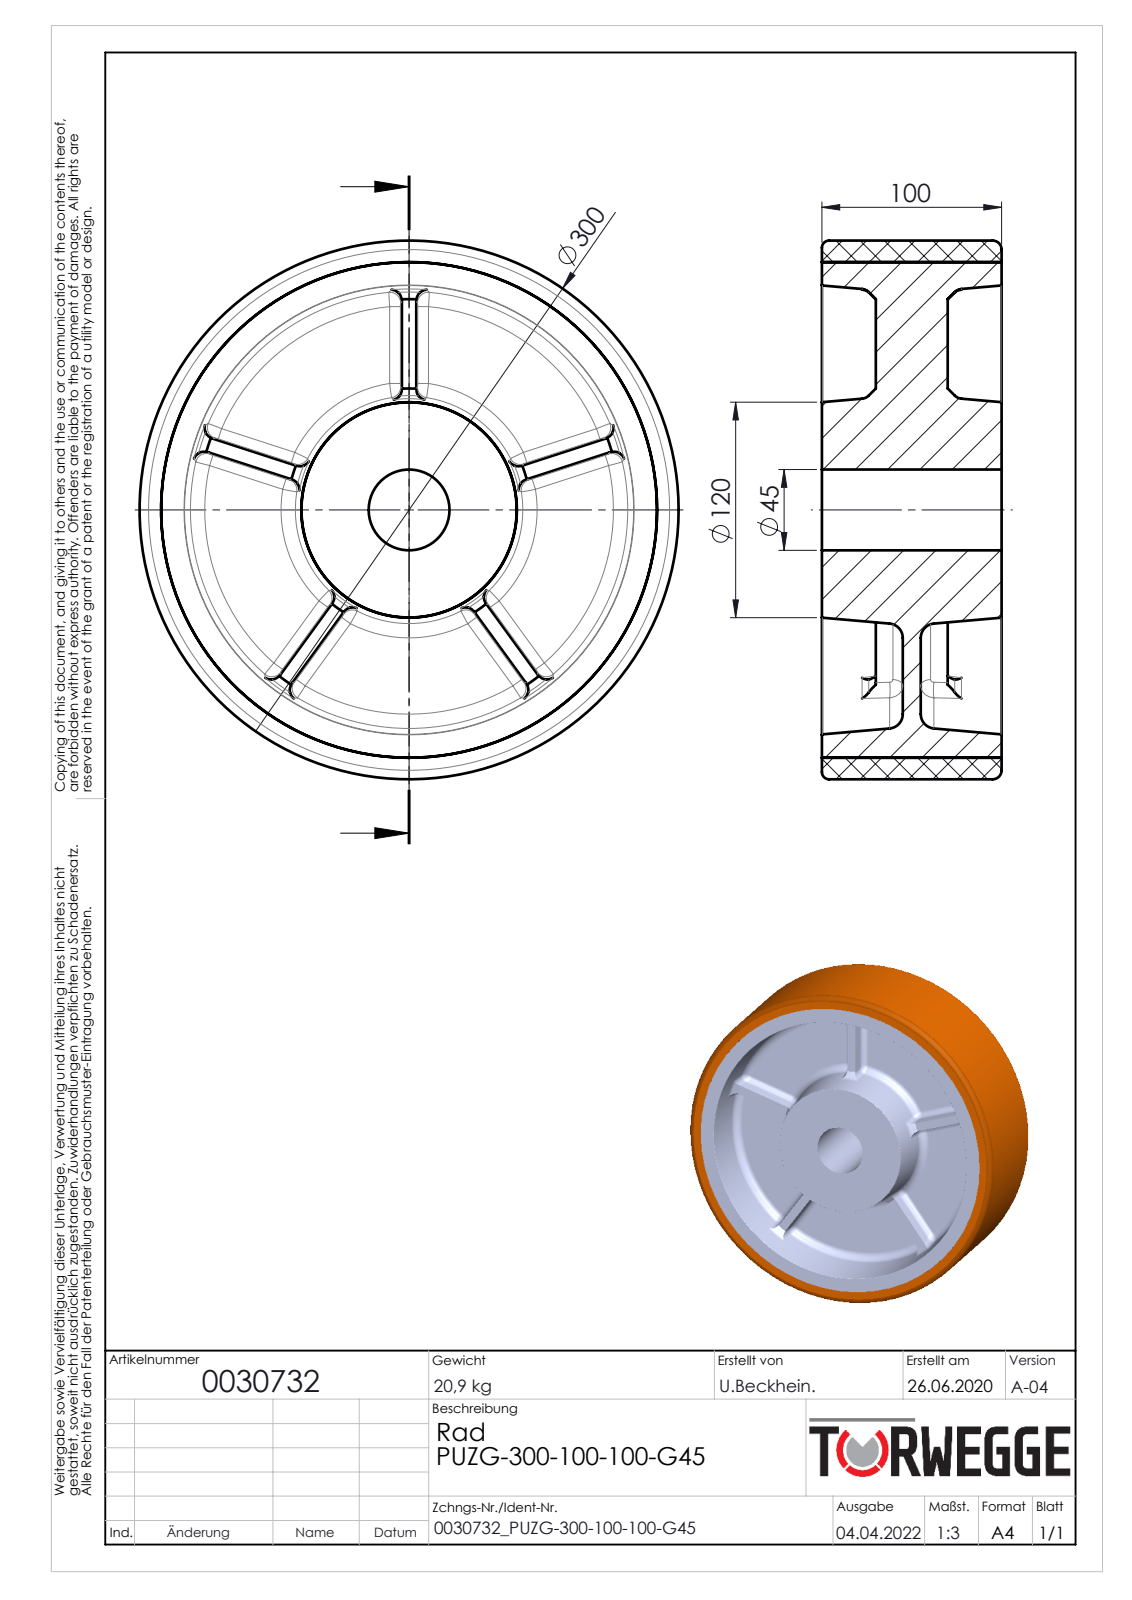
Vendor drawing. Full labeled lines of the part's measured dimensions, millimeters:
Part name (STEP PRODUCT): 0030732
STEP written by: SolidWorks 2020 (AUTOMOTIVE_DESIGN)
Units: millimetres
Bodies: 2 solids, 238 faces (46 planar, 28 cylindrical, 164 other)
Overall size (bounding box): 300 × 300 × 100
Volume: 3 826 000 mm³ · Surface area: 515 290 mm²
Round holes (diameter × count): ⌀45 ×1, ⌀276 ×1
Round bosses / shafts (diameter × count): ⌀300 ×1
Partial cylindrical surfaces — rounded edges, fillets, slot ends (radius × count): R6 ×20
Main face-to-face distances: 45, 55, 100, 10, 30, 70, 15, 25, 11.45, 40
